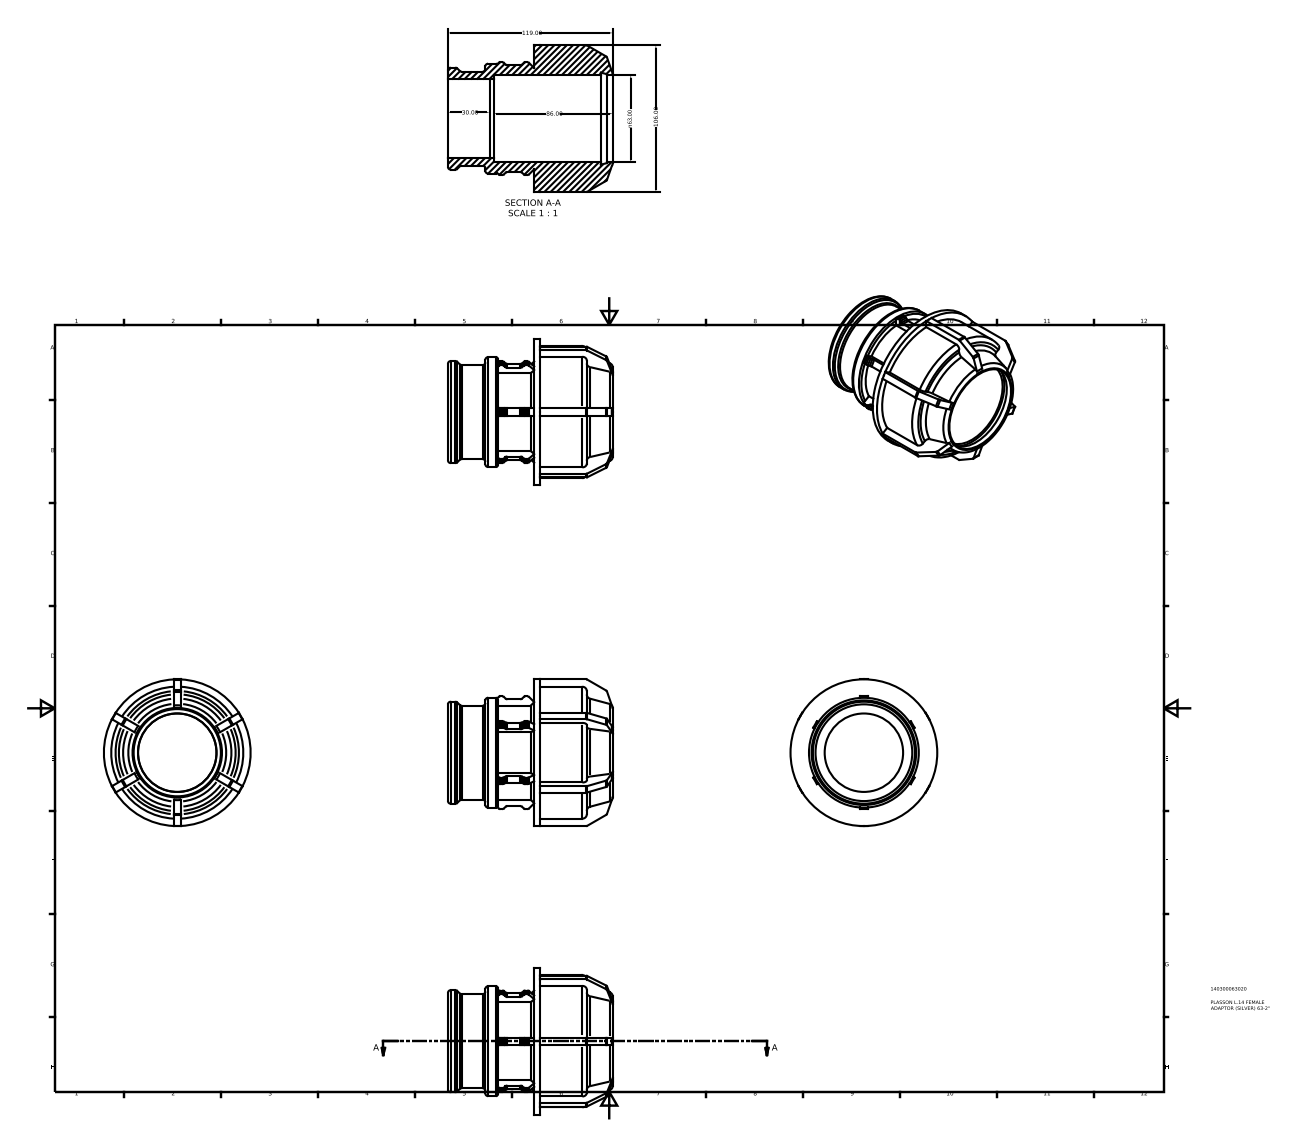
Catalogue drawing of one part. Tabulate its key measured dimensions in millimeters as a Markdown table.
| quantity | value |
| --- | --- |
| part name | 140300063020 |
| STEP written by | Autodesk Inventor 2015 (AUTOMOTIVE_DESIGN) |
| units | millimeters |
| bodies | 1 solid, 262 faces (160 planar, 68 cylindrical, 34 other) |
| overall size | 119 × 106 × 106 |
| volume | 266 467 mm³ |
| surface area | 72 227 mm² |
| round holes (diameter × count) | 56.66 × 1, 56.7 × 1, 63 × 1 |
| round bosses / shafts (diameter × count) | 106 × 1, 95.4 × 1, 79.32 × 1, 73.65 × 1, 67.99 × 1 |
| partial cylindrical surfaces (radius × count) | 1.89 × 48 |
| main face-to-face distances | 5.3, 4.3, 62.24, 66.54, 36, 26.24, 30.54, 3, 33, 29.24 |
